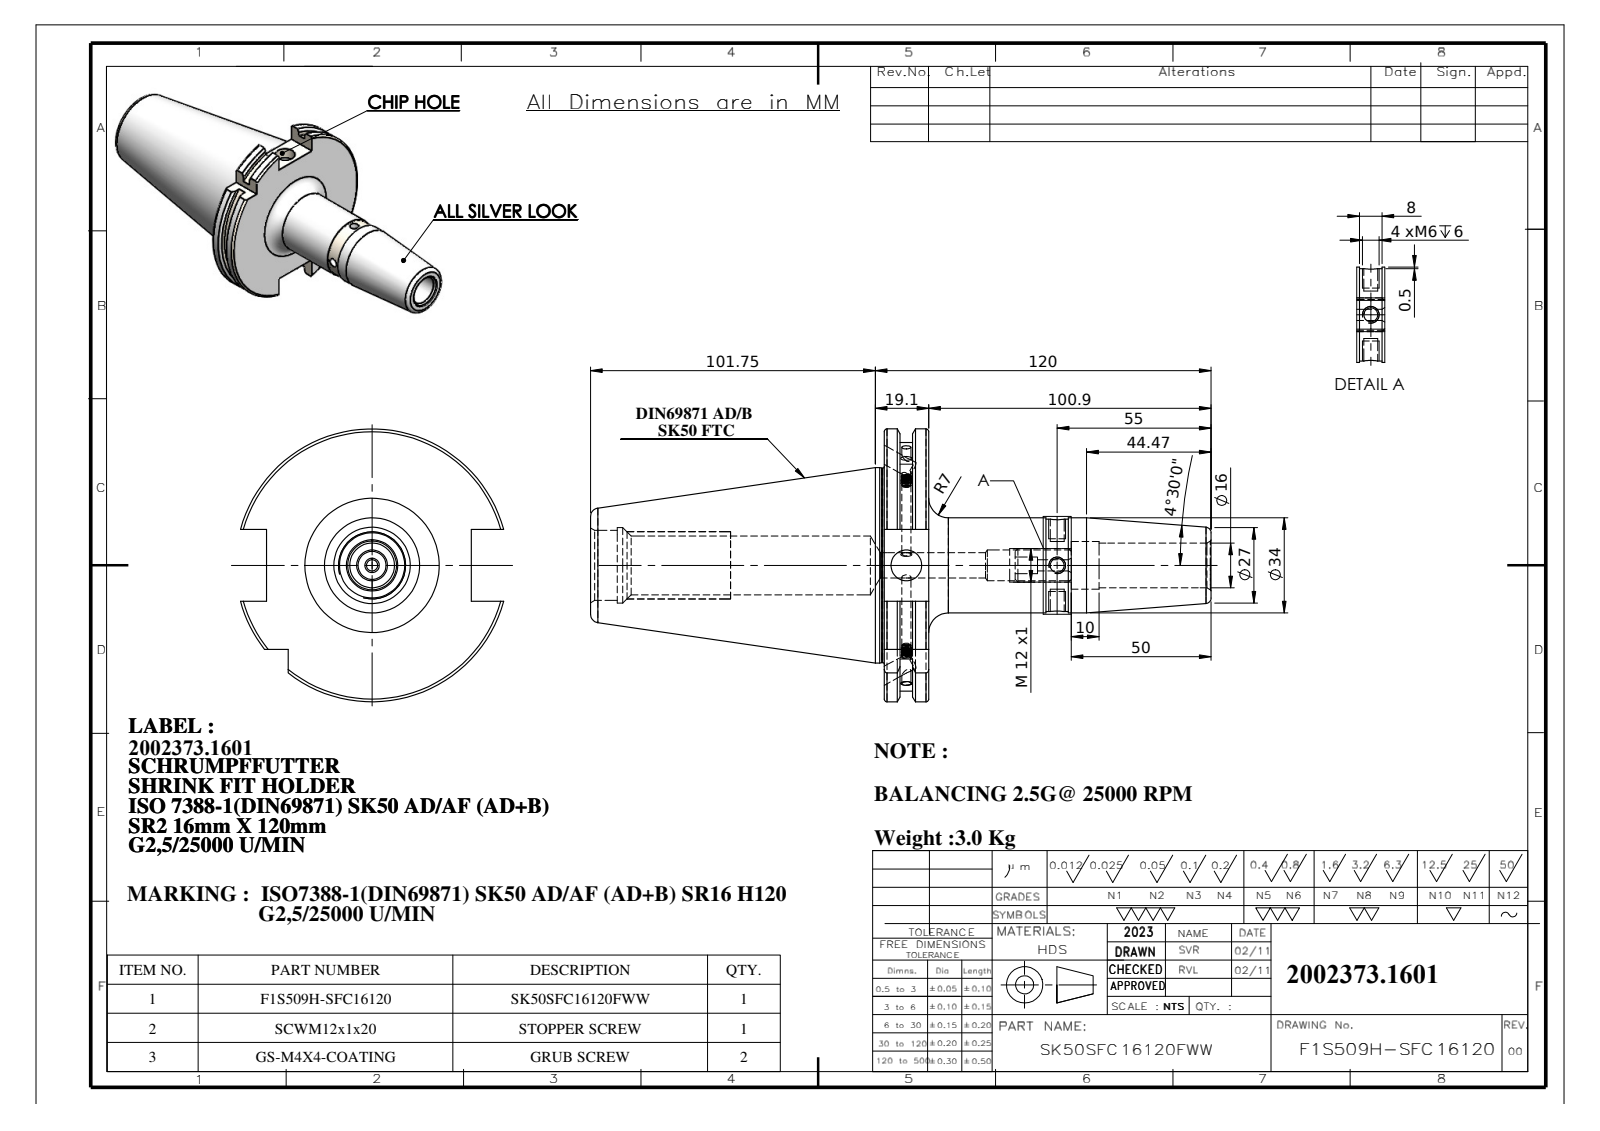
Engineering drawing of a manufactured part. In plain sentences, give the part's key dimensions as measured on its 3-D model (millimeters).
The part is named "91506-SR216120". Its 3-D file was written by "SolidWorks 2018 (AUTOMOTIVE_DESIGN)". It is 1 solid with 126 faces: 25 planar, 53 cylindrical and 48 other. Overall it measures 221.75 by 97.5 by 94.05 millimeters. Its volume is 400 393 cubic millimeters and its surface area 58 108 square millimeters. Round holes: 2 of diameter 5, 2 of diameter 6, 2 of diameter 11, 1 of diameter 3.3, 1 of diameter 15.99, 1 of diameter 17, 1 of diameter 21, 1 of diameter 25, 1 of diameter 27. Round bosses or shafts: 1 of diameter 69.85, 1 of diameter 69.45, 1 of diameter 34. Partial cylindrical surfaces (rounded edges, fillets, slot ends): 1 of radius 44.9, 1 of radius 48.75. The main face-to-face distances are 15.9, 5.66, 10.24, 10.14, 4.48, 5.76, 104.95, 110.61, 115.09, 120.85. The hole center spacings are 53.9.
